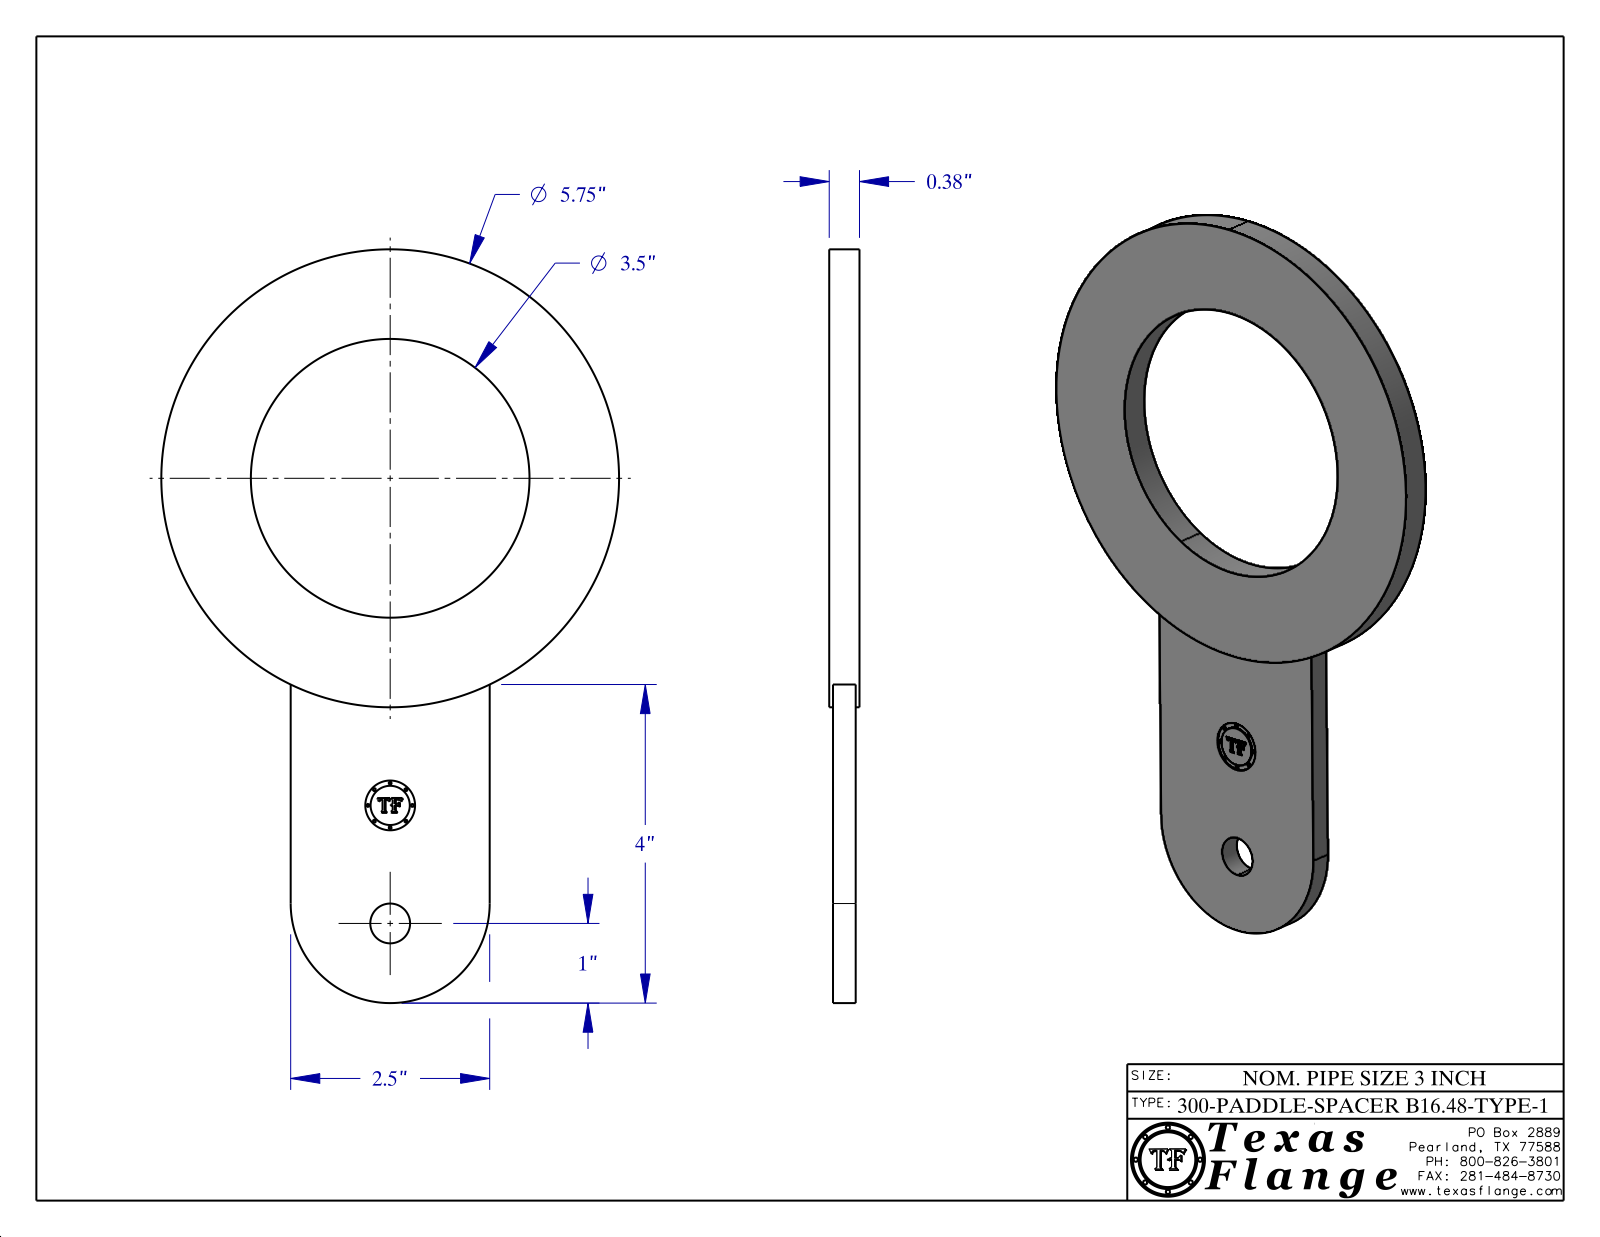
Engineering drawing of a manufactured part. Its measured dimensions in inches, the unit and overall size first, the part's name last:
Units: inches
Overall size (bounding box): 9.464 × 5.75 × 0.38
Round holes (diameter × count): ⌀0.5 ×1, ⌀0.625 ×1, ⌀3.5 ×1
Round bosses / shafts (diameter × count): ⌀0.038 ×8, ⌀5.75 ×1, ⌀0.492 ×1
Partial cylindrical surfaces — rounded edges, fillets, slot ends (radius × count): R1.25 ×1
Main face-to-face distances: 0.048, 0.333, 0.38, 0.285, 2.5, 0.318, 0.27, 0.015, 0.063, 1.187
Hole centre spacings: 1.482, 4.107, 5.589
Volume: 8.675 in³ · Surface area: 63.55 in²
Bodies: 1 solid, 398 faces (371 planar, 27 cylindrical, 0 other)
Part name (STEP PRODUCT): 3-300-PADDLE-SPACER-B16.48-TYPE-2
STEP written by: CATIA V5 STEP AP214 (AUTOMOTIVE_DESIGN)
